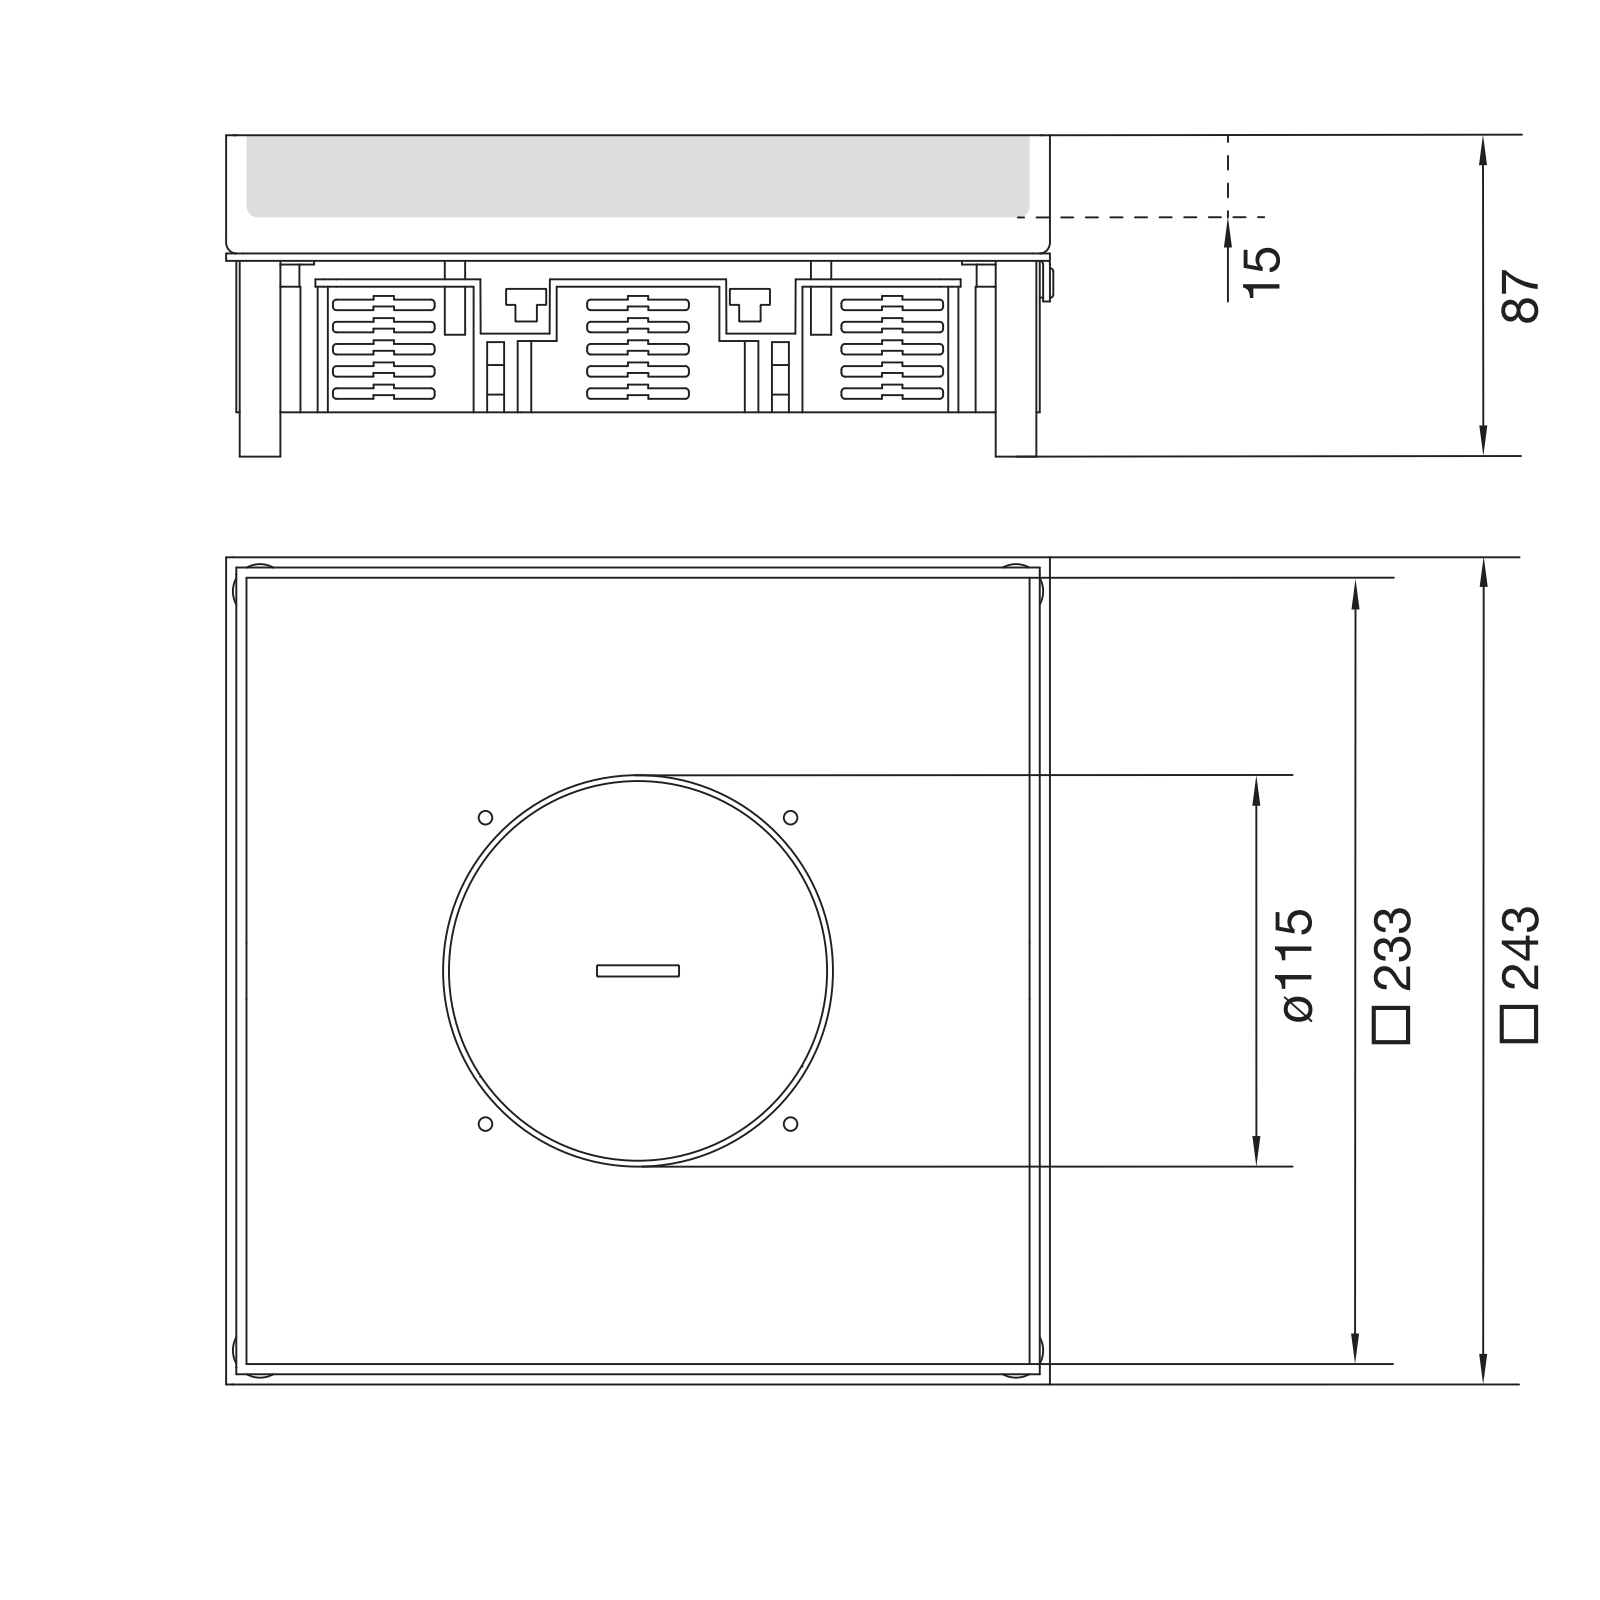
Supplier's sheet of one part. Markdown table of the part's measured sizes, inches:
| quantity | value |
| --- | --- |
| part name | T-00627; T-00632; T-00625; T-00824_ASM (+8 more) |
| STEP written by | CREO PARAMETRIC BY PTC INC, 2022024 (AUTOMOTIVE_DESIGN) |
| units | inches |
| bodies | 11 solids, 261 faces (144 planar, 107 cylindrical, 10 other) |
| overall size | 9.567 × 9.567 × 3.425 |
| volume | 49.89 in³ |
| surface area | 706.8 in² |
| round holes (diameter × count) | 0.197 × 4, 0.268 × 4, 0.335 × 4, 0.177 × 3, 3.173 × 1, 3.543 × 1, 3.976 × 1, 4.213 × 1, 4.276 × 1, 4.409 × 1, 4.425 × 1, 4.606 × 1 |
| round bosses / shafts (diameter × count) | 0.472 × 4, 0.388 × 4, 4.528 × 1, 4.37 × 1, 4.134 × 1, 3.843 × 1 |
| partial cylindrical surfaces (radius × count) | 0.039 × 8, 0.118 × 8, 0.079 × 4, 0.197 × 3, 1.693 × 1, 5.906 × 1, 6.004 × 1 |
| main face-to-face distances | 0.079, 0.118, 0.472, 0.394, 0.098, 9.252, 0.138, 0.197, 9.232, 0.236 |
| hole center spacings | 6.694, 2.506, 3.543, 3.703, 6.208, 8.713, 8.78, 2.126 |
